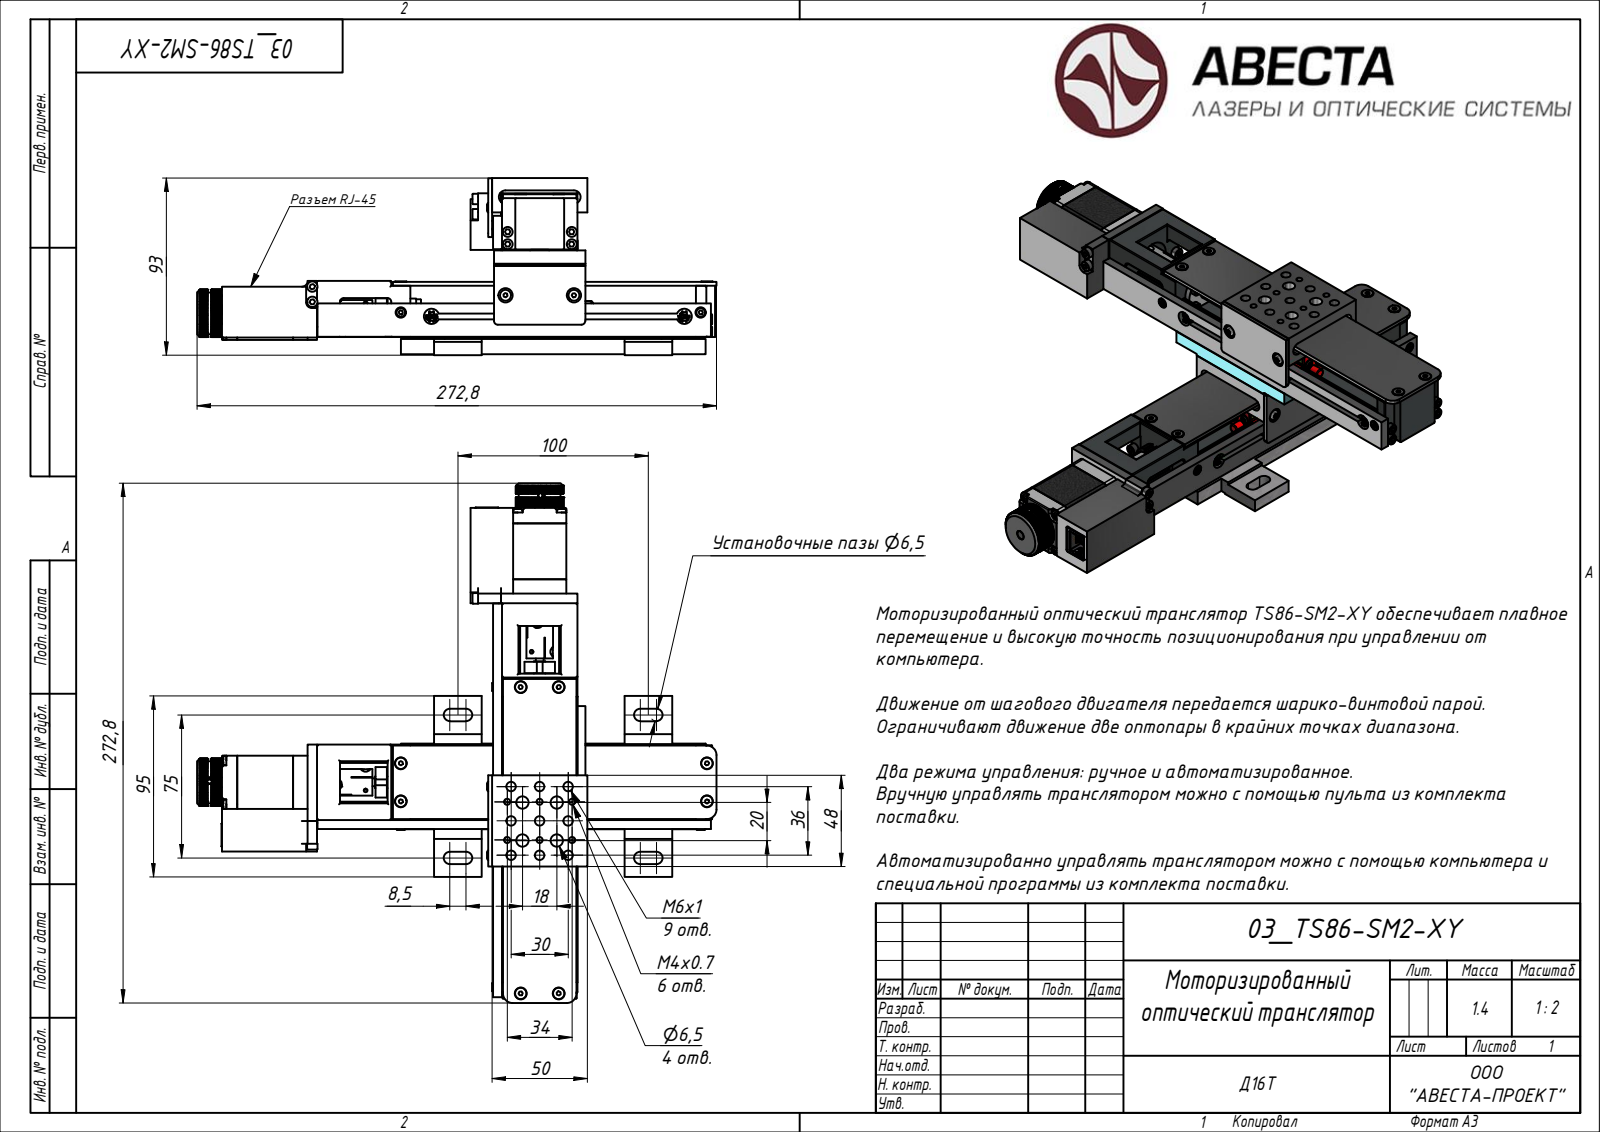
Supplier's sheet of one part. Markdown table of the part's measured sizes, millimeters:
| quantity | value |
| --- | --- |
| STEP written by | Rhino 7.34 (AUTOMOTIVE_DESIGN) |
| units | millimeters |
| bodies | 1 solid, 4667 faces (2841 planar, 1276 cylindrical, 550 other) |
| overall size | 272.8 × 272.8 × 93 |
| volume | 535 733 mm³ |
| surface area | 227 114 mm² |
| round holes (diameter × count) | 3.4 × 28, 6.5 × 20, 2.5 × 14, 2.46 × 13, 4.92 × 13, 3.24 × 12, 1.05 × 10, 7.5 × 10, 5 × 8, 2.15 × 6, 4.92 × 5, 2.9 × 4 |
| round bosses / shafts (diameter × count) | 4.5 × 20, 5.5 × 12, 6 × 10, 5.3 × 8, 3 × 8, 2.5 × 8, 5 × 6, 5.7 × 4 |
| partial cylindrical surfaces (radius × count) | 0.5 × 72, 2.5 × 20, 3 × 20, 2 × 16, 1 × 8, 3.25 × 8, 1.75 × 4, 2.4 × 4 |
| main face-to-face distances | 46, 0.5, 2, 2.5, 38, 46.5, 5, 27.5, 5.5, 29.5 |
| hole center spacings | 20, 1, 26, 247, 2, 9, 13.04, 18 |
